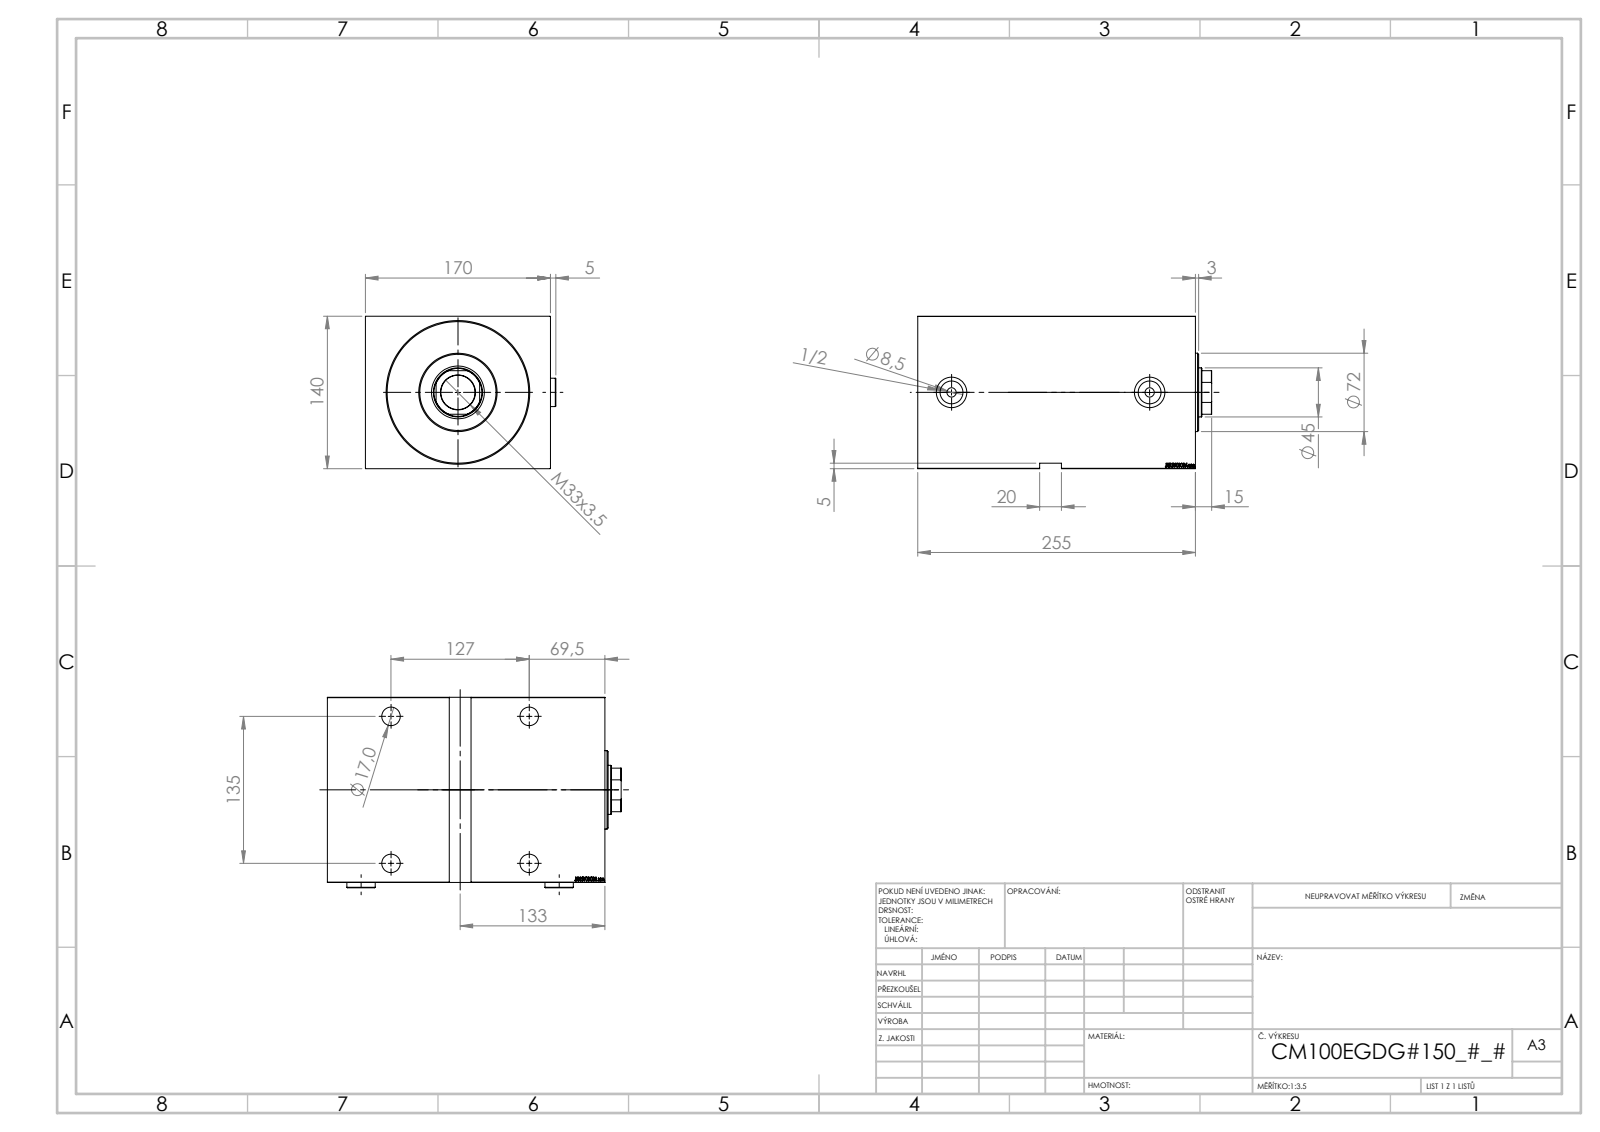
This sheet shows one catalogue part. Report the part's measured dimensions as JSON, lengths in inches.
{"part_name": "Zatka_OIL_PORT; V450CM_E_VCP; V450CM_E_Body; V450CM_VC_B", "step_written_by": "SolidWorks 2019 (CONFIG_CONTROL_DESIGN)", "units": "inches", "bodies": {"solids": 5, "faces": 912, "planar": 446, "cylindrical": 68, "other": 398}, "overall_size": [10.63, 6.886, 5.512], "volume_in3": 301.8, "surface_area_in2": 644.8, "round_holes": [[0.669, 4], [0.984, 4], [0.335, 2], [0.825, 2], [1.102, 2], [1.24, 1], [1.772, 1], [1.909, 1], [3.937, 1], [5.118, 1]], "round_bosses_or_shafts": [[1.024, 2], [4.016, 1], [2.835, 1]], "partial_cylinders_radius": [[0.866, 1]], "face_to_face_distances": [5.512, 6.693, 10.039, 1.024, 9.016, 0.197, 9.843, 8.819, 3.543, 9.386], "hole_center_spacings": [5, 5.315, 7.297, 7.165]}
